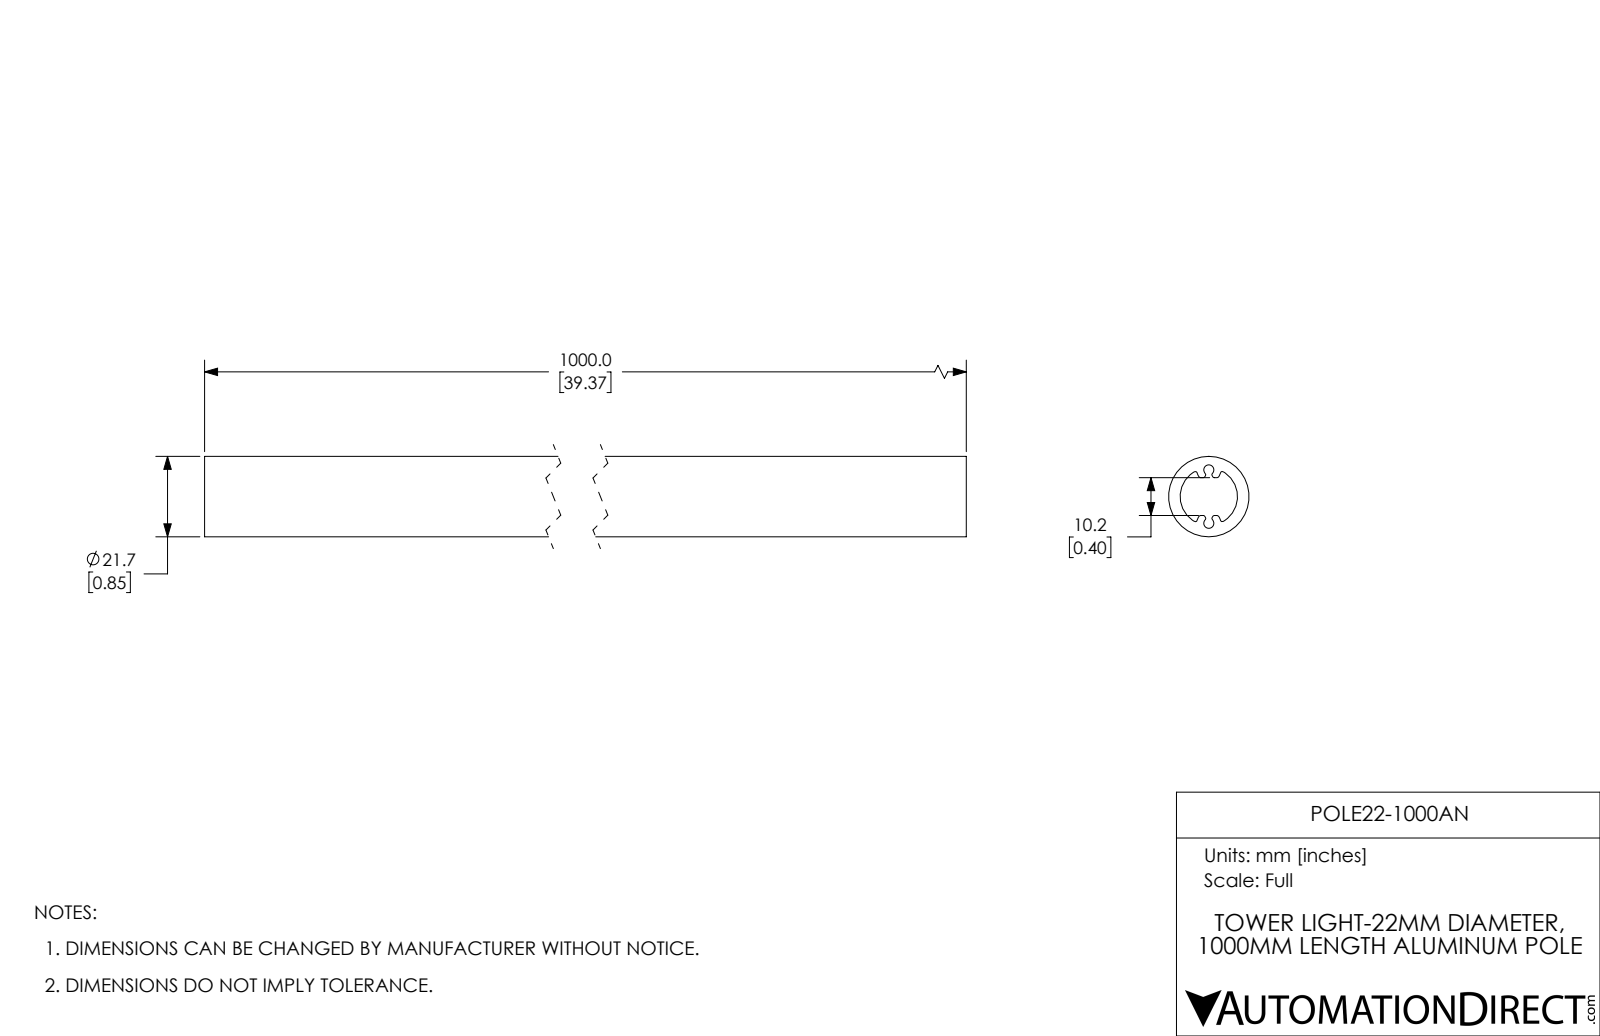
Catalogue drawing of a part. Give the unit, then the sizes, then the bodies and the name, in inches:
Units: inches
Overall size (bounding box): 39.37 × 0.854 × 0.854
Round bosses / shafts (diameter × count): ⌀0.854 ×1
Main face-to-face distances: 39.37
Volume: 11.94 in³ · Surface area: 206.5 in²
Bodies: 1 solid, 8 faces (2 planar, 2 cylindrical, 4 other)
Part name (STEP PRODUCT): POLE22-1000AN
STEP written by: SolidWorks 2017 (AUTOMOTIVE_DESIGN)
